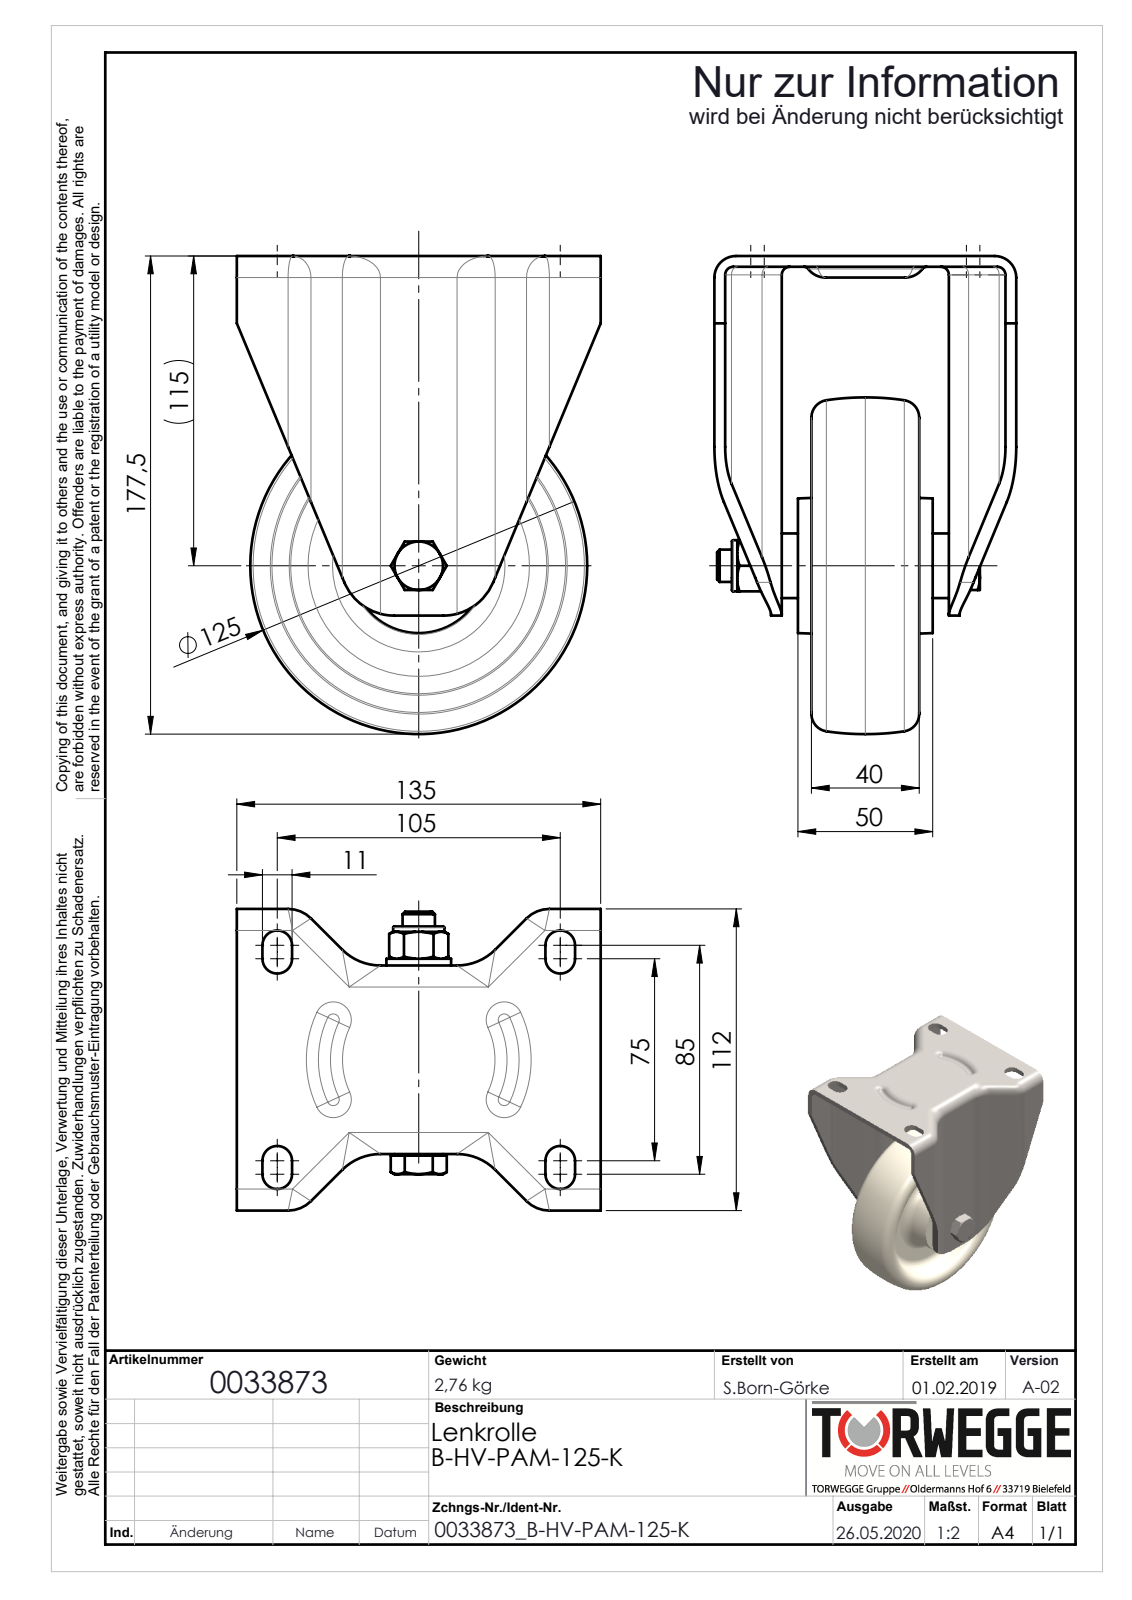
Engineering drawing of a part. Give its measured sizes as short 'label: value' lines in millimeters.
name: 0033873
written by: SolidWorks 2018 (AUTOMOTIVE_DESIGN)
unit: mm
bodies: 0 solids, 295 faces (85 planar, 90 cylindrical, 120 other)
size: 177.5 × 135 × 112
holes: 1× ⌀10.2, 1× ⌀12.1, 1× ⌀12.3, 1× ⌀13, 1× ⌀15, 1× ⌀16, 1× ⌀29
bosses: 1× ⌀24, 1× ⌀21, 1× ⌀19, 1× ⌀18, 1× ⌀14.95, 1× ⌀12
rounds: 12× R8, 8× R3, 8× R5.5, 6× R20, 4× R12, 4× R25
face distances: 4, 30, 66, 21, 87, 13.68, 10, 26, 40, 36
